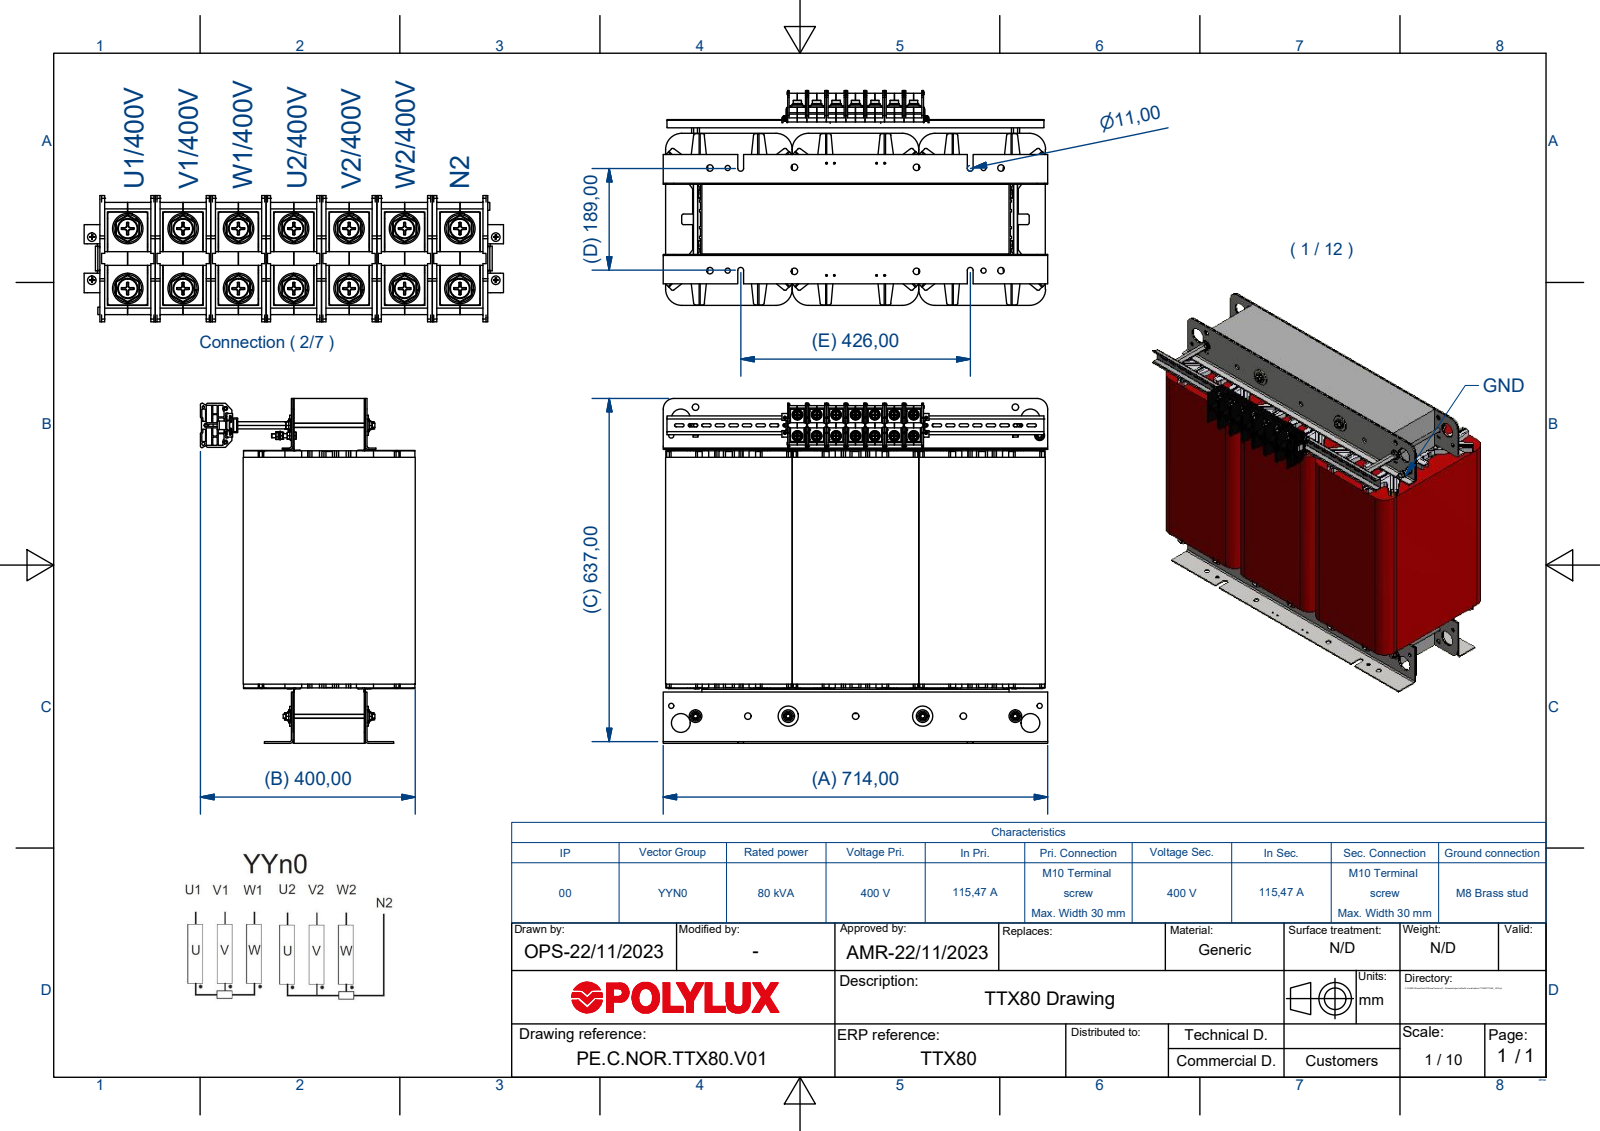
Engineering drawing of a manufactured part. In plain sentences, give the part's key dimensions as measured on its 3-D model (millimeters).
The part is named "TTX80_V02". Its 3-D file was written by "Autodesk Inventor 2018 (AUTOMOTIVE_DESIGN)". It is 218 solids with 10708 faces: 8120 planar, 1935 cylindrical and 653 other. Overall it measures 714 by 640 by 398.45 millimeters. Its volume is 105 700 000 cubic millimeters and its surface area 7 471 000 square millimeters. Round holes: 26 of diameter 12, 14 of diameter 8.3, 14 of diameter 10.5, 14 of diameter 10.7, 14 of diameter 12.25, 10 of diameter 11.5, 9 of diameter 6.65, 9 of diameter 8.4, 8 of diameter 3.5, 8 of diameter 9, 6 of diameter 11.25, 4 of diameter 13. Round bosses or shafts: 14 of diameter 20, 14 of diameter 18.1, 14 of diameter 9.85, 9 of diameter 8, 8 of diameter 24, 4 of diameter 37, 4 of diameter 3.92, 4 of diameter 3. Partial cylindrical surfaces (rounded edges, fillets, slot ends): 206 of radius 0.5, 180 of radius 1, 100 of radius 2, 60 of radius 3.5, 58 of radius 3, 48 of radius 1.55, 16 of radius 3.75, 14 of radius 0.93. The main face-to-face distances are 235, 2, 132, 130, 470, 92.75, 94.75, 224.75, 226.75, 67.5. The hole center spacings are 540, 250, 15, 30.21, 32.5, 33.5, 34.6, 36.21.
